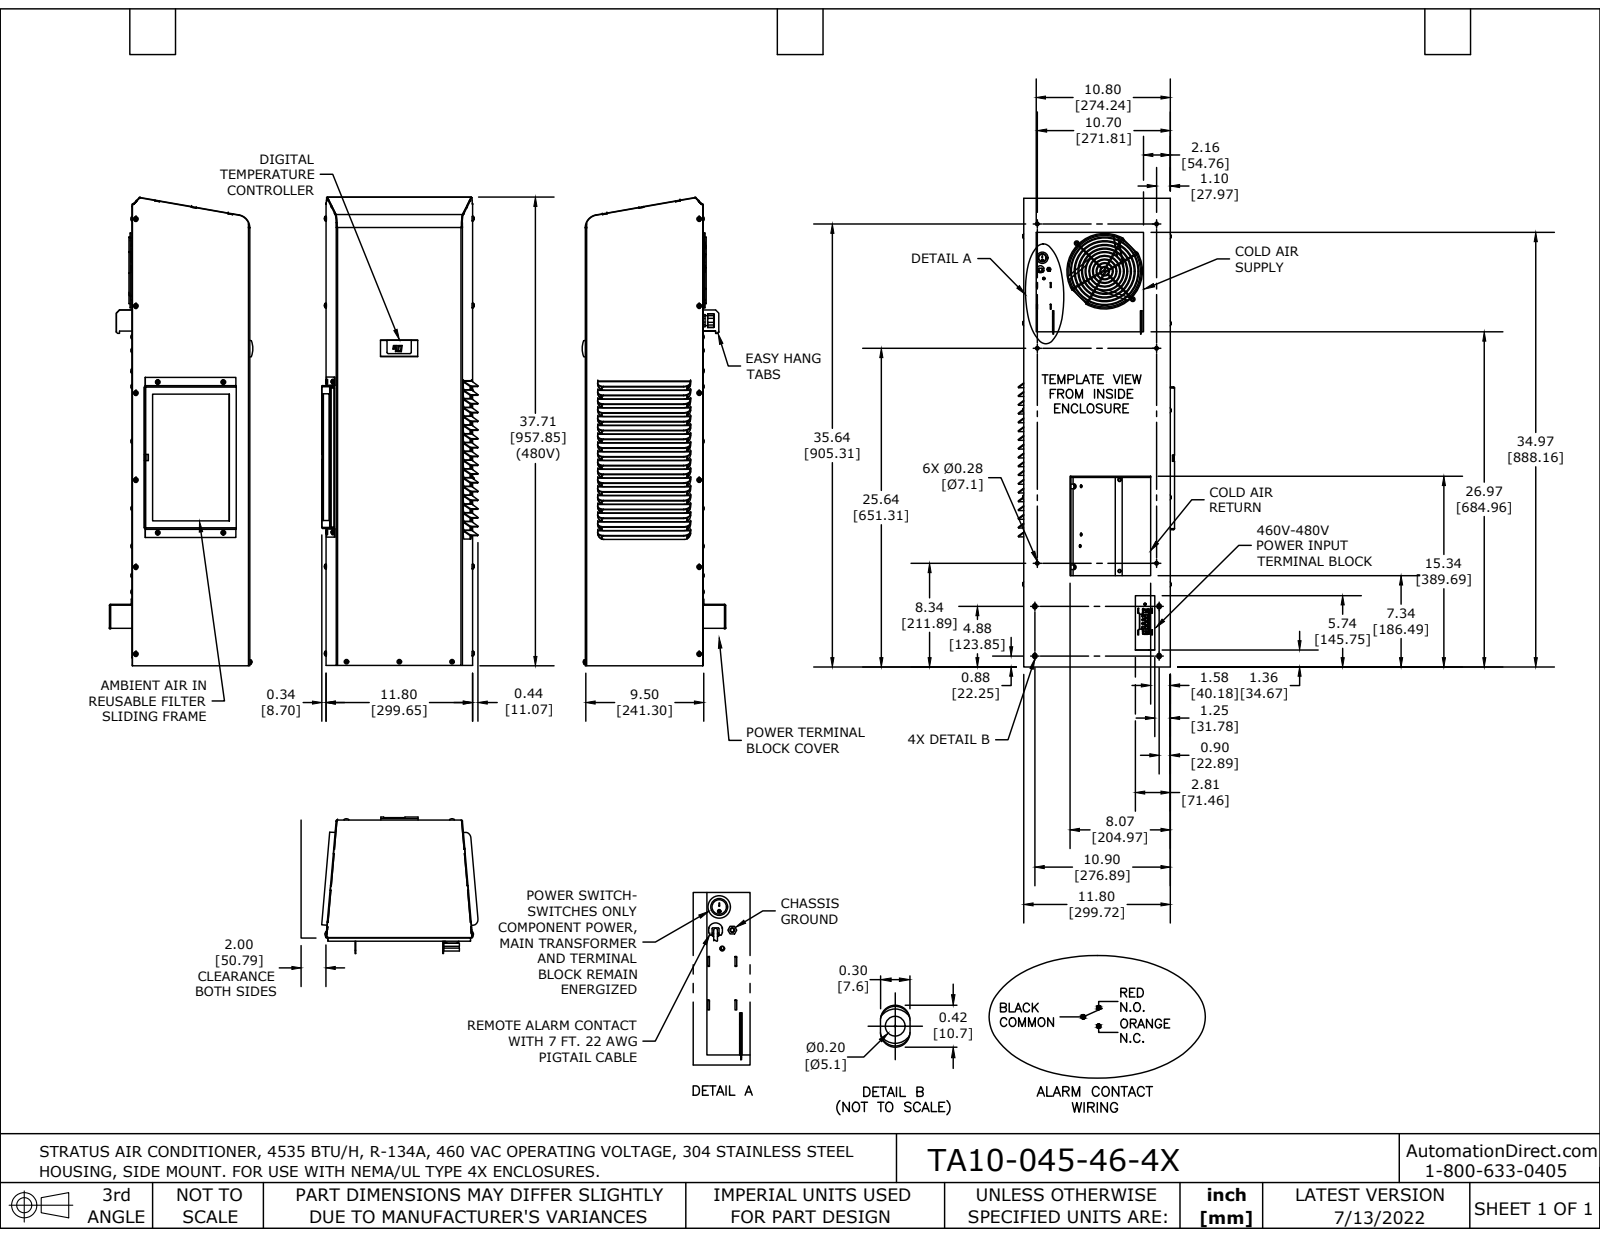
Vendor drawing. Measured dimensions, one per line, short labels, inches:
name: TA10-045-46-4X
written by: SolidWorks 2021 (AUTOMOTIVE_DESIGN)
unit: in
bodies: 1 solid, 1744 faces (1077 planar, 497 cylindrical, 170 other)
size: 32.024 × 12.576 × 11.549
volume: 136.5 in³; area: 3 197 in²
holes: 11× ⌀0.159, 5× ⌀0.204, 1× ⌀6
bosses: 7× ⌀0.19, 2× ⌀0.379, 2× ⌀0.353, 2× ⌀0.248, 1× ⌀6.07, 1× ⌀0.906, 1× ⌀0.087
rounds: 45× R0.015, 42× R0.01, 36× R0.5, 36× R0.506, 28× R0.1, 21× R0.058, 21× R0.116, 13× R0.03
face distances: 0.058, 9.435, 9.377, 0.058, 9.493, 0.09, 0.25, 0.308, 9.685, 9.743
hole spacings: 7, 14, 21, 1.732, 5.3, 6.565, 10.869, 12.12
